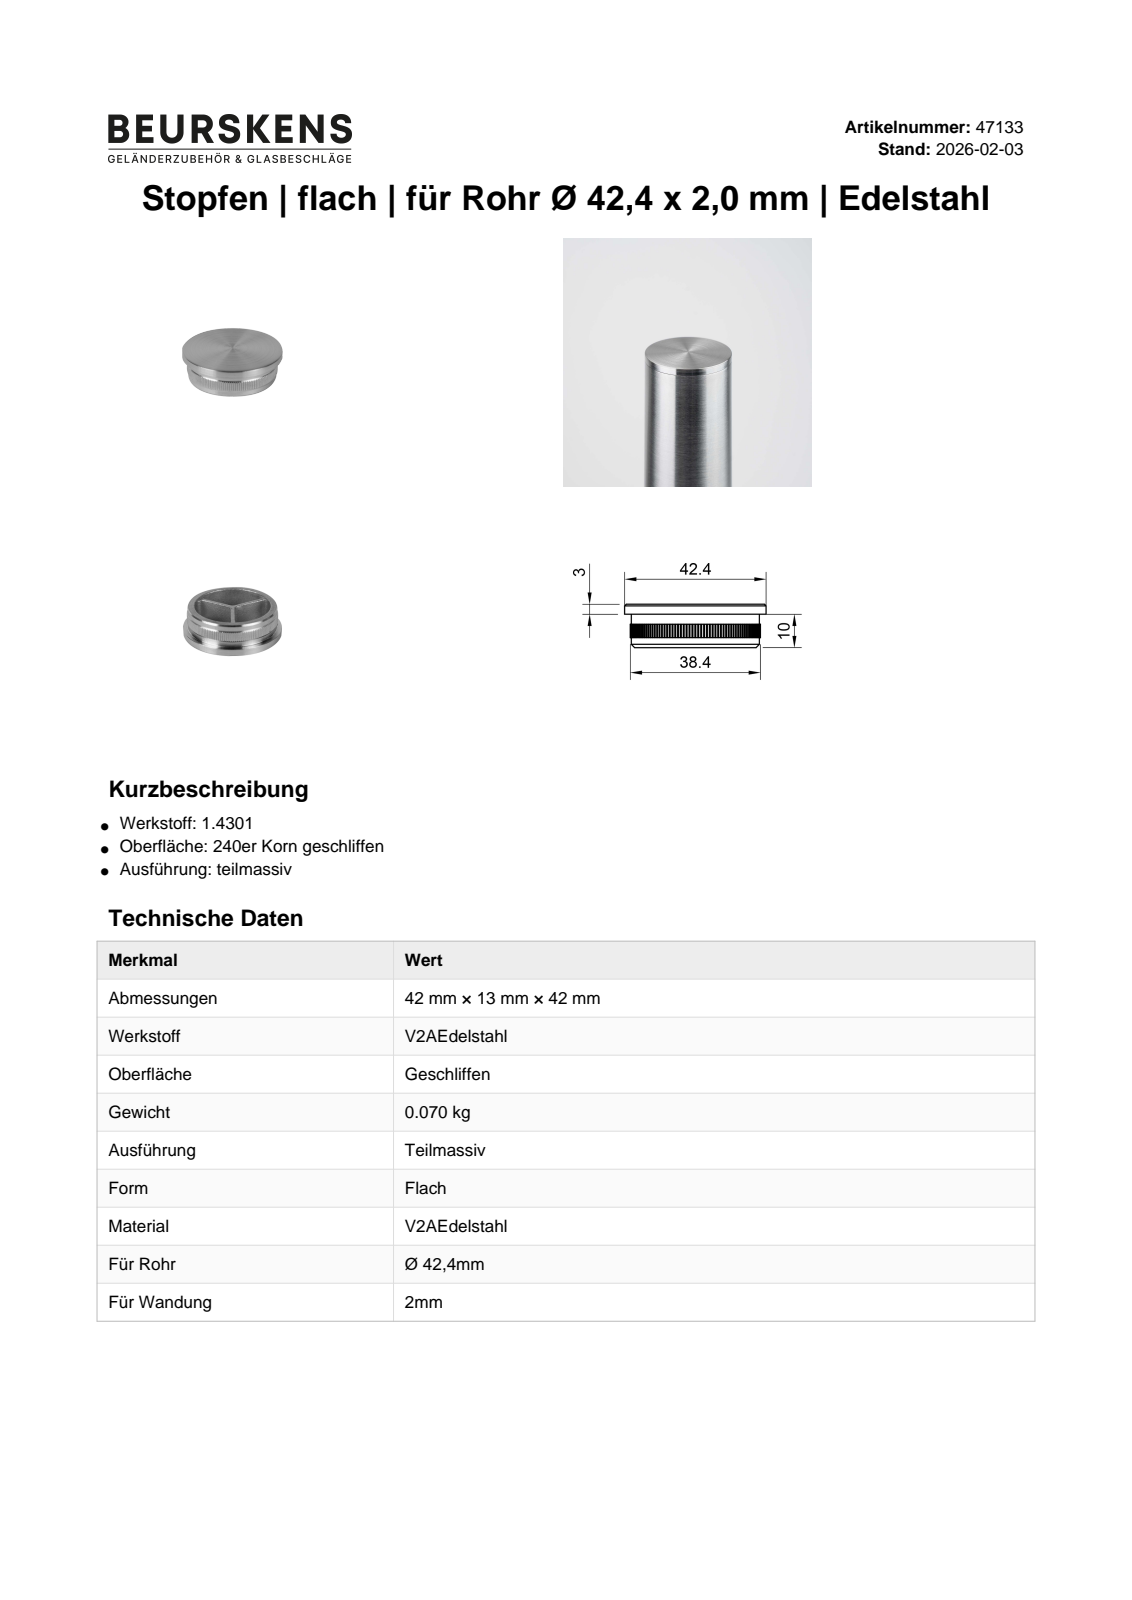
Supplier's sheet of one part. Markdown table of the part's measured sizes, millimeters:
| quantity | value |
| --- | --- |
| part name | 47133 |
| STEP written by | Autodesk Inventor 2022 (AUTOMOTIVE_DESIGN) |
| units | millimeters |
| bodies | 1 solid, 292 faces (6 planar, 284 cylindrical, 2 other) |
| overall size | 42.4 × 42.4 × 13 |
| volume | 8 326 mm³ |
| surface area | 5 446 mm² |
| round holes (diameter × count) | 31 × 1 |
| round bosses / shafts (diameter × count) | 42.4 × 1, 38.4 × 1 |
| partial cylindrical surfaces (radius × count) | 0.12 × 140, 19.5 × 1 |
| main face-to-face distances | 3, 10, 13, 7, 4, 6 |
